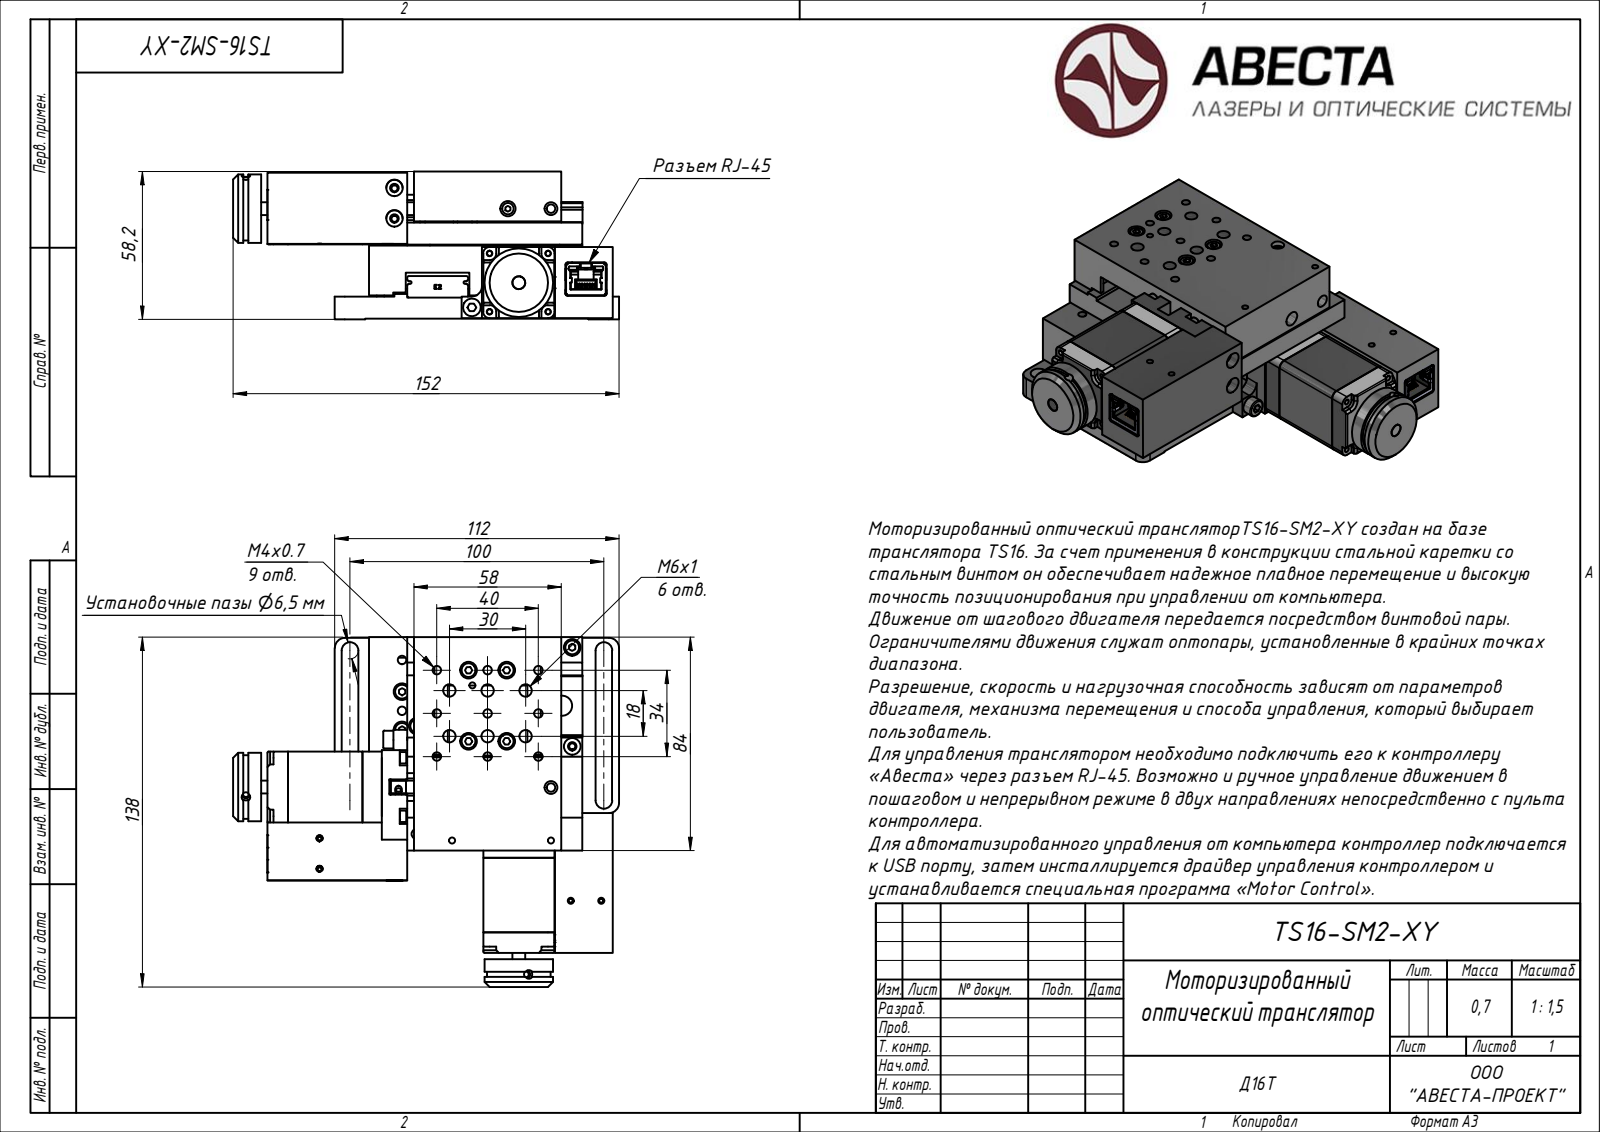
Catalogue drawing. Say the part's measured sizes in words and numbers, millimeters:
The part is named "Block 01". Its 3-D file was written by "ST-DEVELOPER v15 (AUTOMOTIVE_DESIGN)". It is 41 solids with 4190 faces: 0 planar, 0 cylindrical and 4190 other. Overall it measures 152 by 137.75 by 58.2 millimeters.
